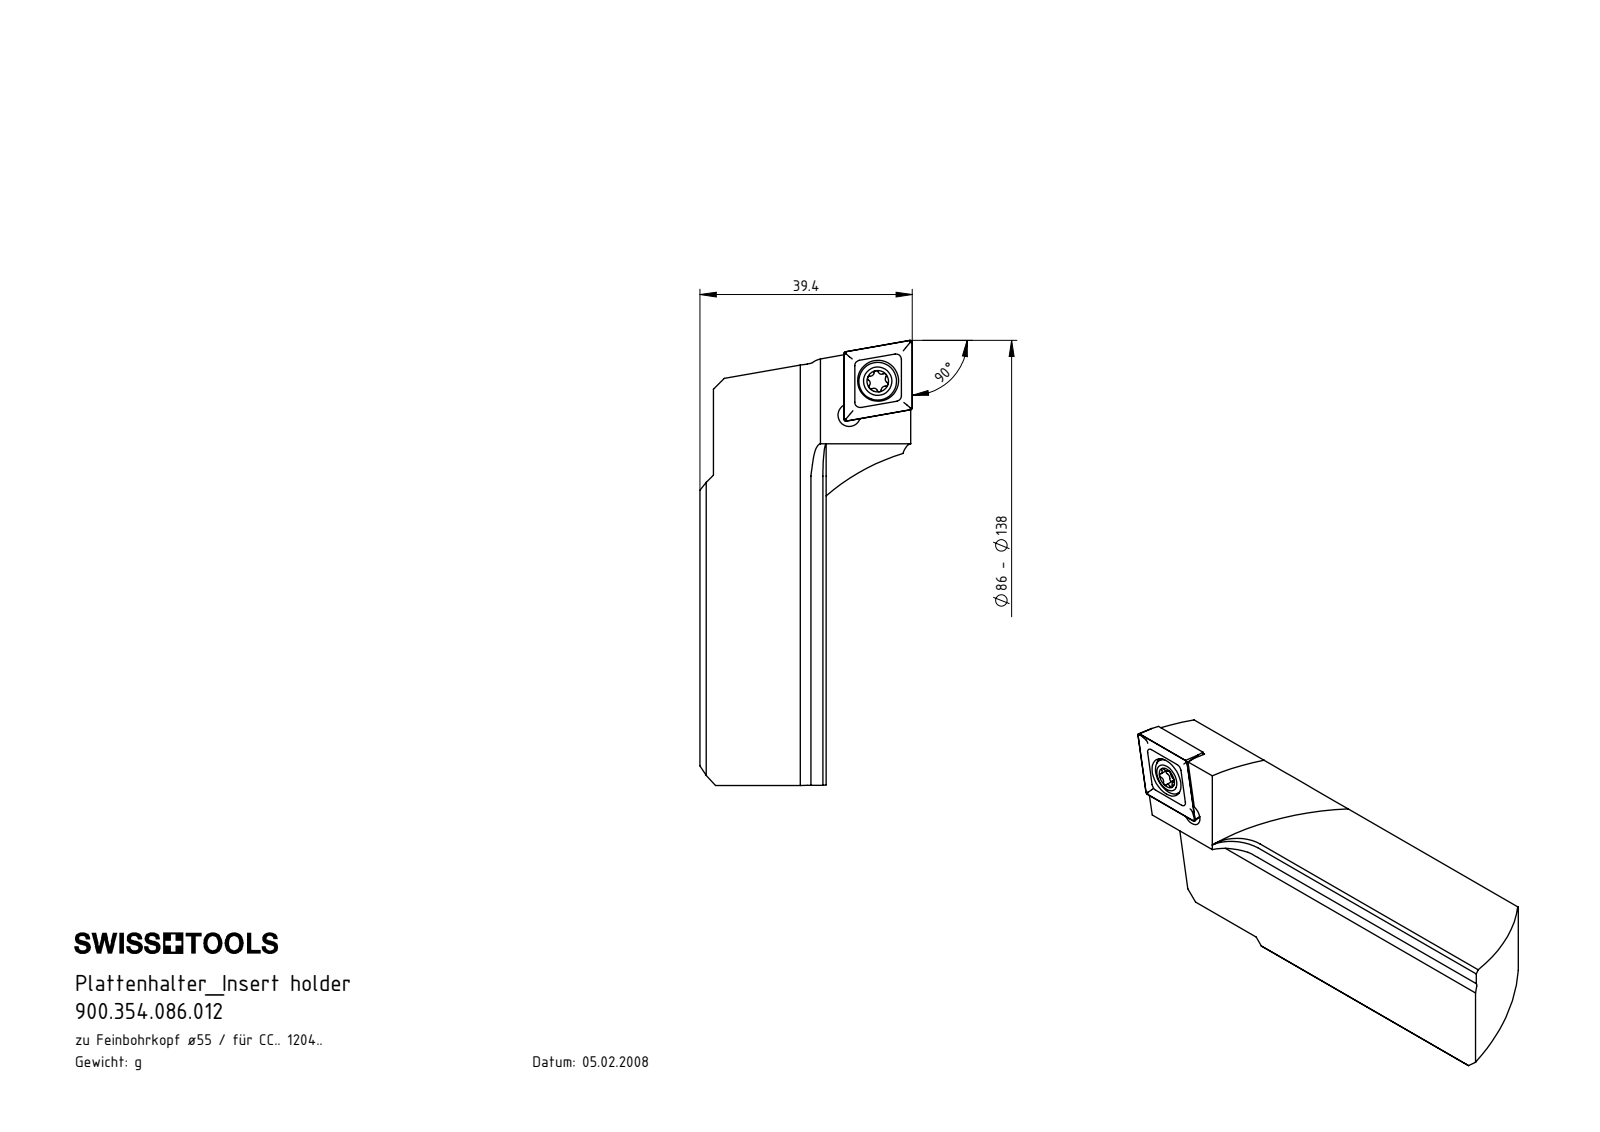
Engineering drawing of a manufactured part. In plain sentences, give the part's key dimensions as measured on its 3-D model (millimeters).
The part is named "F00-WCC.086.001_C; WCC-ER2.001.010_A; CCMT120404; 900.354.086.012". Its 3-D file was written by "SolidWorks 2017 (CONFIG_CONTROL_DESIGN)". It is 3 solids with 379 faces: 226 planar, 40 cylindrical and 113 other. Overall it measures 82.58 by 39.4 by 27.35 millimeters. Its volume is 33 749 cubic millimeters and its surface area 9 364 square millimeters. Round holes: 2 of diameter 4.2, 1 of diameter 5.5, 1 of diameter 7.6. Round bosses or shafts: 1 of diameter 7, 1 of diameter 5. Partial cylindrical surfaces (rounded edges, fillets, slot ends): 8 of radius 0.2, 6 of radius 0.39, 3 of radius 0.69, 3 of radius 0.69, 3 of radius 40, 1 of radius 0.8, 1 of radius 6. The main face-to-face distances are 2.38, 21.3, 4.76, 7.14, 9.52, 4.77, 7.15, 9.53, 11.91, 14.29. The hole center spacings are 8.21, 8.33.
